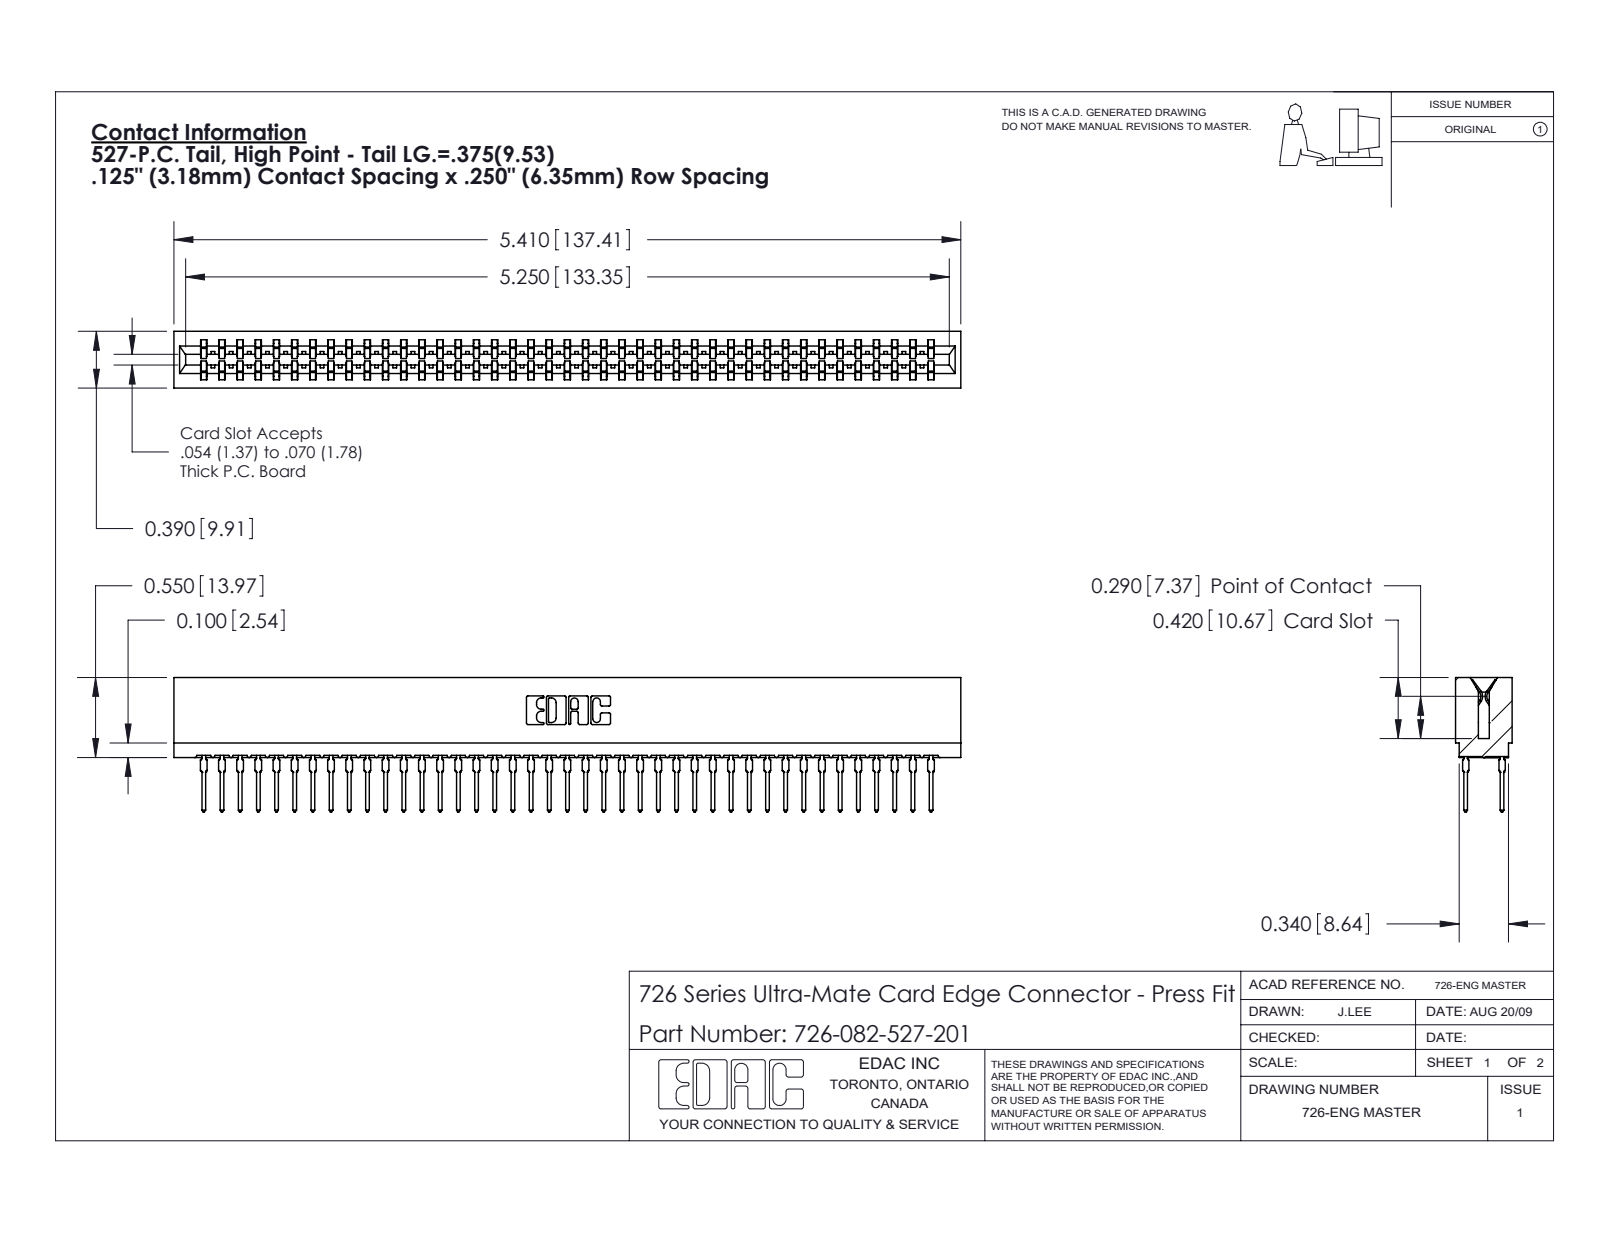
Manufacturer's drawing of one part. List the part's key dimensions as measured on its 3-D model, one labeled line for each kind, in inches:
Part name (STEP PRODUCT): 726 Part_.515 Slot Depth - 01; 726-082-527-201; 746-292-001_527
STEP written by: SolidWorks 2020 (CONFIG_CONTROL_DESIGN)
Units: inches
Bodies: 83 solids, 7436 faces (3827 planar, 1477 cylindrical, 2132 other)
Overall size (bounding box): 5.41 × 0.924 × 0.39
Volume: 0.78 in³ · Surface area: 34 in²
Partial cylindrical surfaces — rounded edges, fillets, slot ends (radius × count): R0.021 ×164, R0.015 ×42, R0.01 ×22, R0.005 ×8, R0.011 ×8, R0.007 ×6, R0.031 ×6, R0.026 ×3
Main face-to-face distances: 0.057, 0.333, 0.025, 0.307, 0.39, 0.25, 0.275, 0.083, 0.365, 0.032
